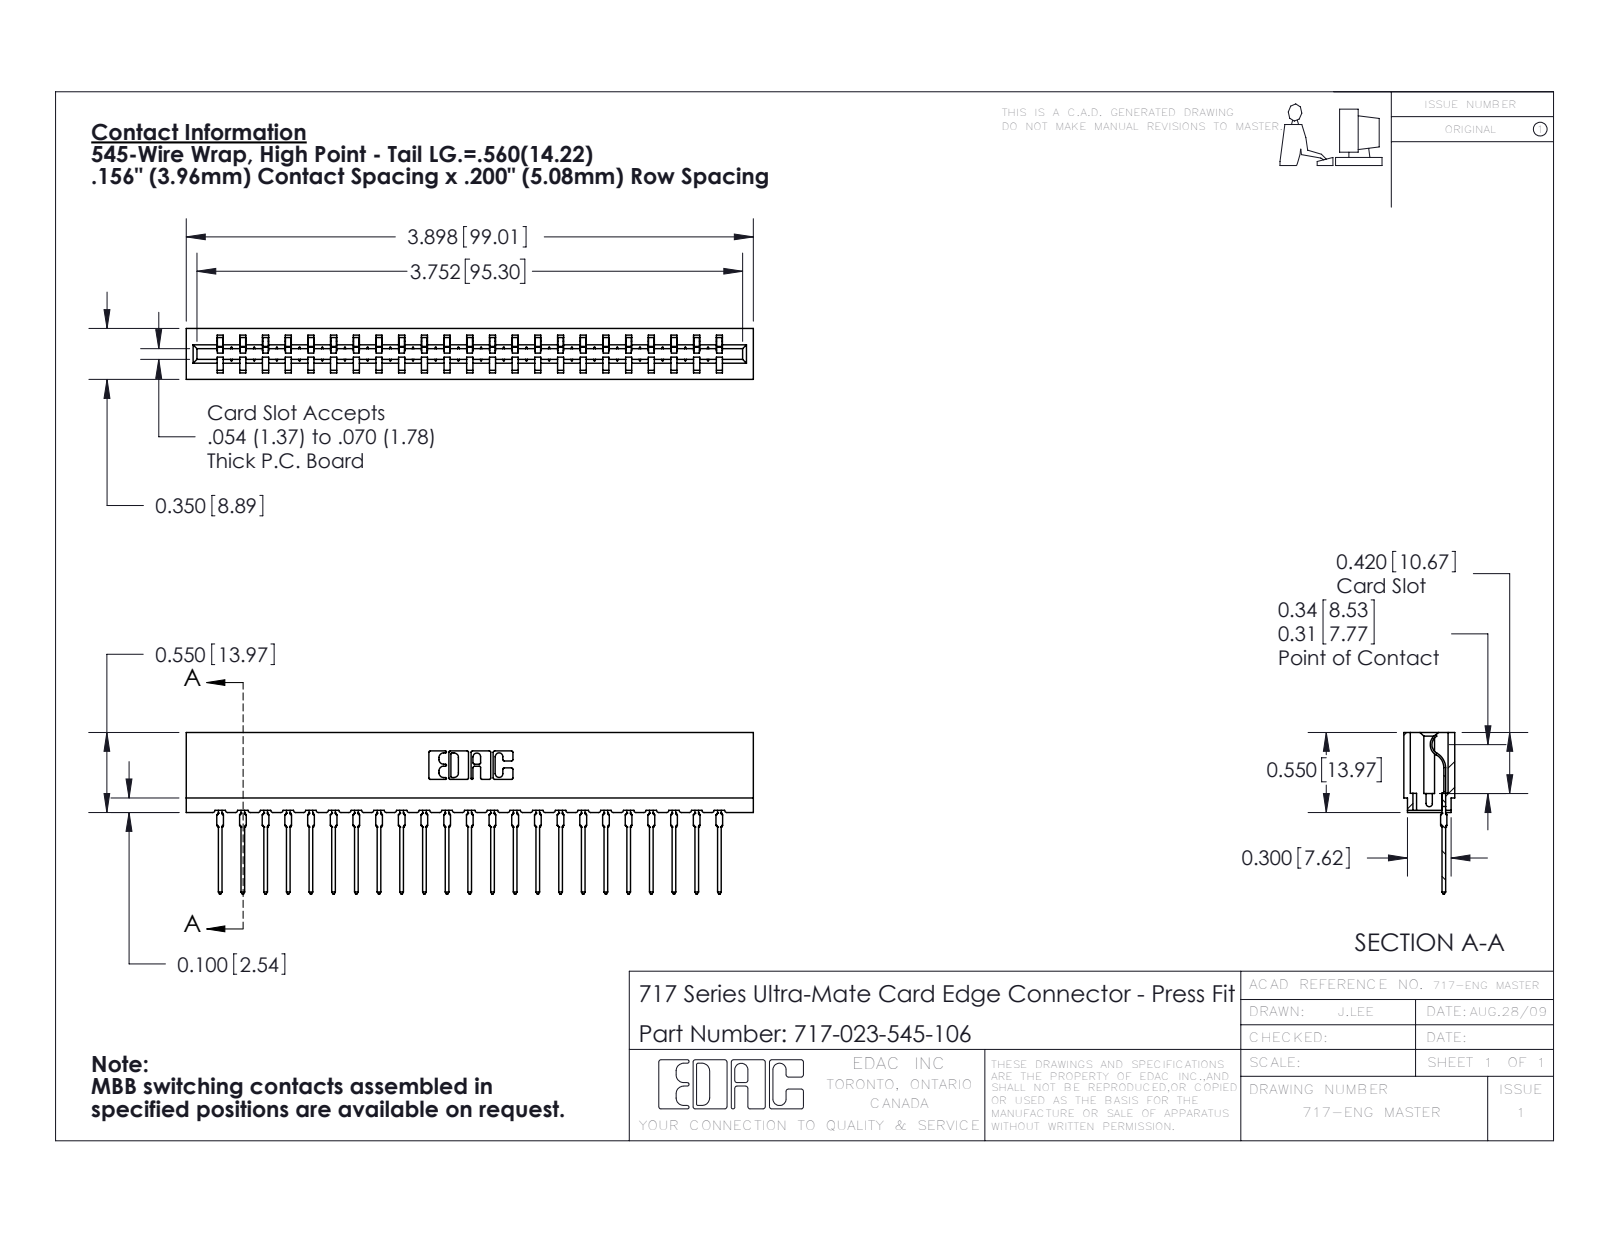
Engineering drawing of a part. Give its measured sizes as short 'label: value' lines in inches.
name: 717 Part_Insulator Option - 06; 745-292-001_545; 717-023-545-106
written by: SolidWorks 2016 (CONFIG_CONTROL_DESIGN)
unit: in
bodies: 24 solids, 2693 faces (1618 planar, 477 cylindrical, 598 other)
size: 3.898 × 1.109 × 0.35
volume: 0.519 in³; area: 18.77 in²
rounds: 46× R0.015, 46× R0.021, 22× R0.01, 6× R0.007, 6× R0.031, 4× R0.005, 4× R0.011, 3× R0.026
face distances: 0.212, 0.138, 0.35, 0.156, 0.074, 0.063, 0.287, 0.076, 0.149, 0.624
